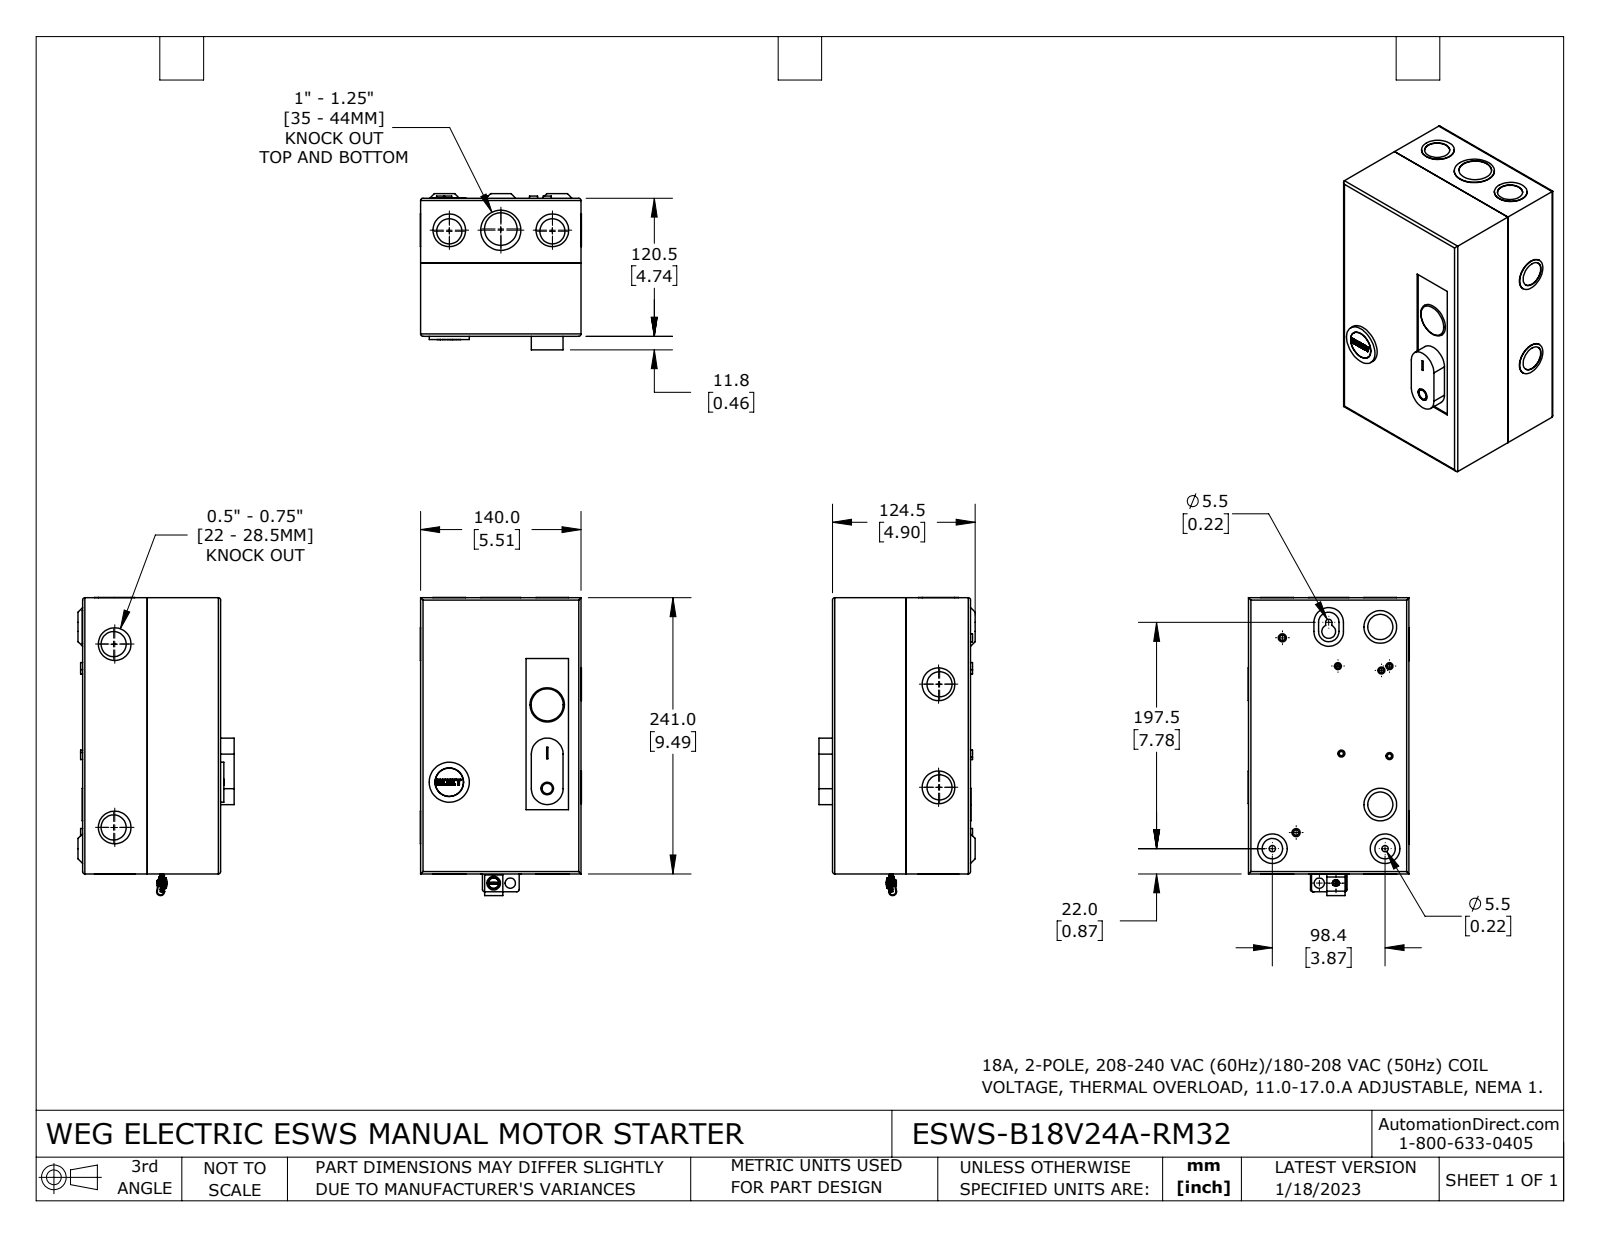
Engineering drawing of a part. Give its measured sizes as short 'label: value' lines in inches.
name: ESWS-B18V24A-RM32
written by: SolidWorks 2021 (CONFIG_CONTROL_DESIGN)
unit: in
bodies: 7 solids, 435 faces (168 planar, 230 cylindrical, 37 other)
size: 10.248 × 5.535 × 5.366
volume: 16.23 in³; area: 585.2 in²
holes: 5× ⌀0.146, 4× ⌀0.864, 2× ⌀0.183, 2× ⌀0.217, 2× ⌀0.354, 2× ⌀0.864, 2× ⌀0.866, 2× ⌀0.886, 1× ⌀0.256, 1× ⌀0.303, 1× ⌀0.433, 1× ⌀0.469
bosses: 6× ⌀1.124, 5× ⌀0.24, 2× ⌀1.122, 2× ⌀0.278, 1× ⌀1.38, 1× ⌀1.378, 1× ⌀1.193, 1× ⌀1.148
rounds: 34× R0.004, 13× R0.079, 4× R0.031, 3× R0.108, 2× R0.059, 2× R0.075, 2× R0.122, 2× R0.138
face distances: 0.047, 4.697, 5.465, 4.65, 9.441, 4.744, 5.417, 5.512, 0.071, 0.063
hole spacings: 0.571, 1.378, 1.773, 3.387, 3.543, 4.921, 5.995, 7.484
